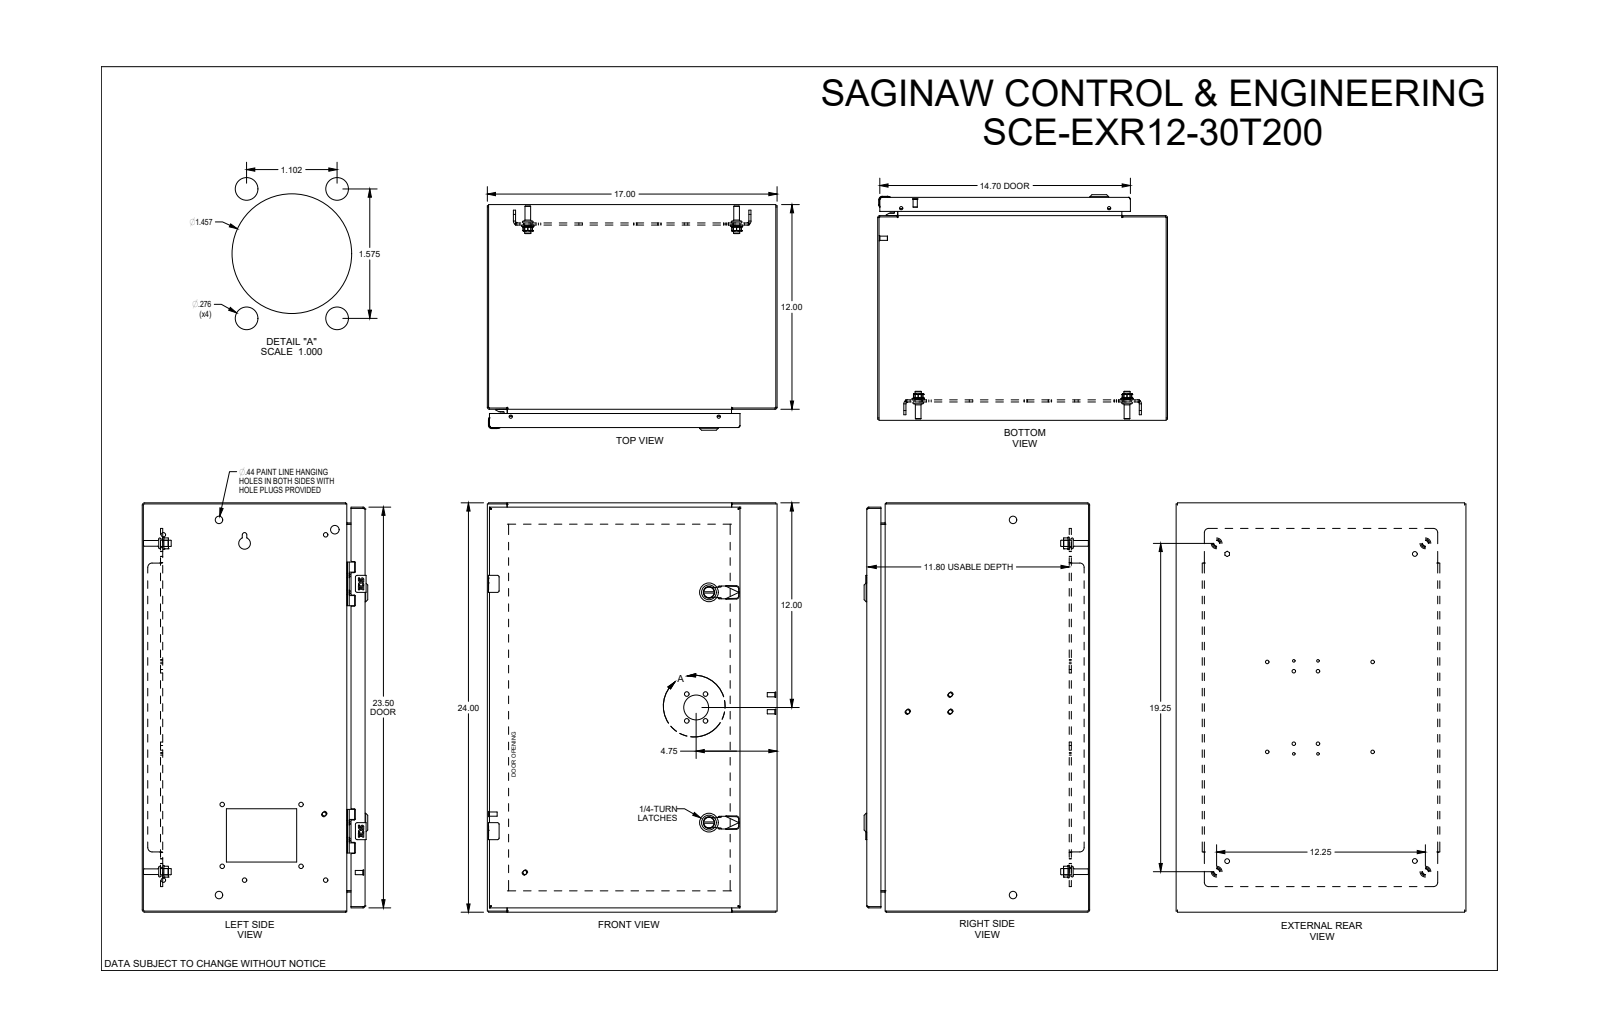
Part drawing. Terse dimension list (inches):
name: SCE-EXR12-30T200
written by: SolidWorks 2019 (CONFIG_CONTROL_DESIGN)
unit: in
bodies: 0 solids, 2298 faces (1135 planar, 731 cylindrical, 432 other)
size: 24 × 17 × 13.23
holes: 13× ⌀0.266, 8× ⌀0.203, 6× ⌀0.156, 5× ⌀0.5, 4× ⌀0.172, 4× ⌀0.205, 4× ⌀0.244, 4× ⌀0.367, 4× ⌀0.375, 3× ⌀0.28, 2× ⌀0.04, 2× ⌀0.197
bosses: 6× ⌀0.17, 5× ⌀0.248, 4× ⌀0.366, 4× ⌀0.332, 4× ⌀0.276, 4× ⌀0.25, 4× ⌀0.24, 3× ⌀0.196
rounds: 56× R0.012, 40× R0.015, 24× R0.01, 20× R0.02, 14× R0.025, 14× R0.117, 12× R0.042, 12× R0.1
face distances: 0.075, 0.075, 12.998, 16.925, 23.925, 12.923, 13.073, 1, 1.125, 11.923
hole spacings: 14.5, 0.985, 0.02, 0.493, 0.494, 1.417, 4.625, 9.338
